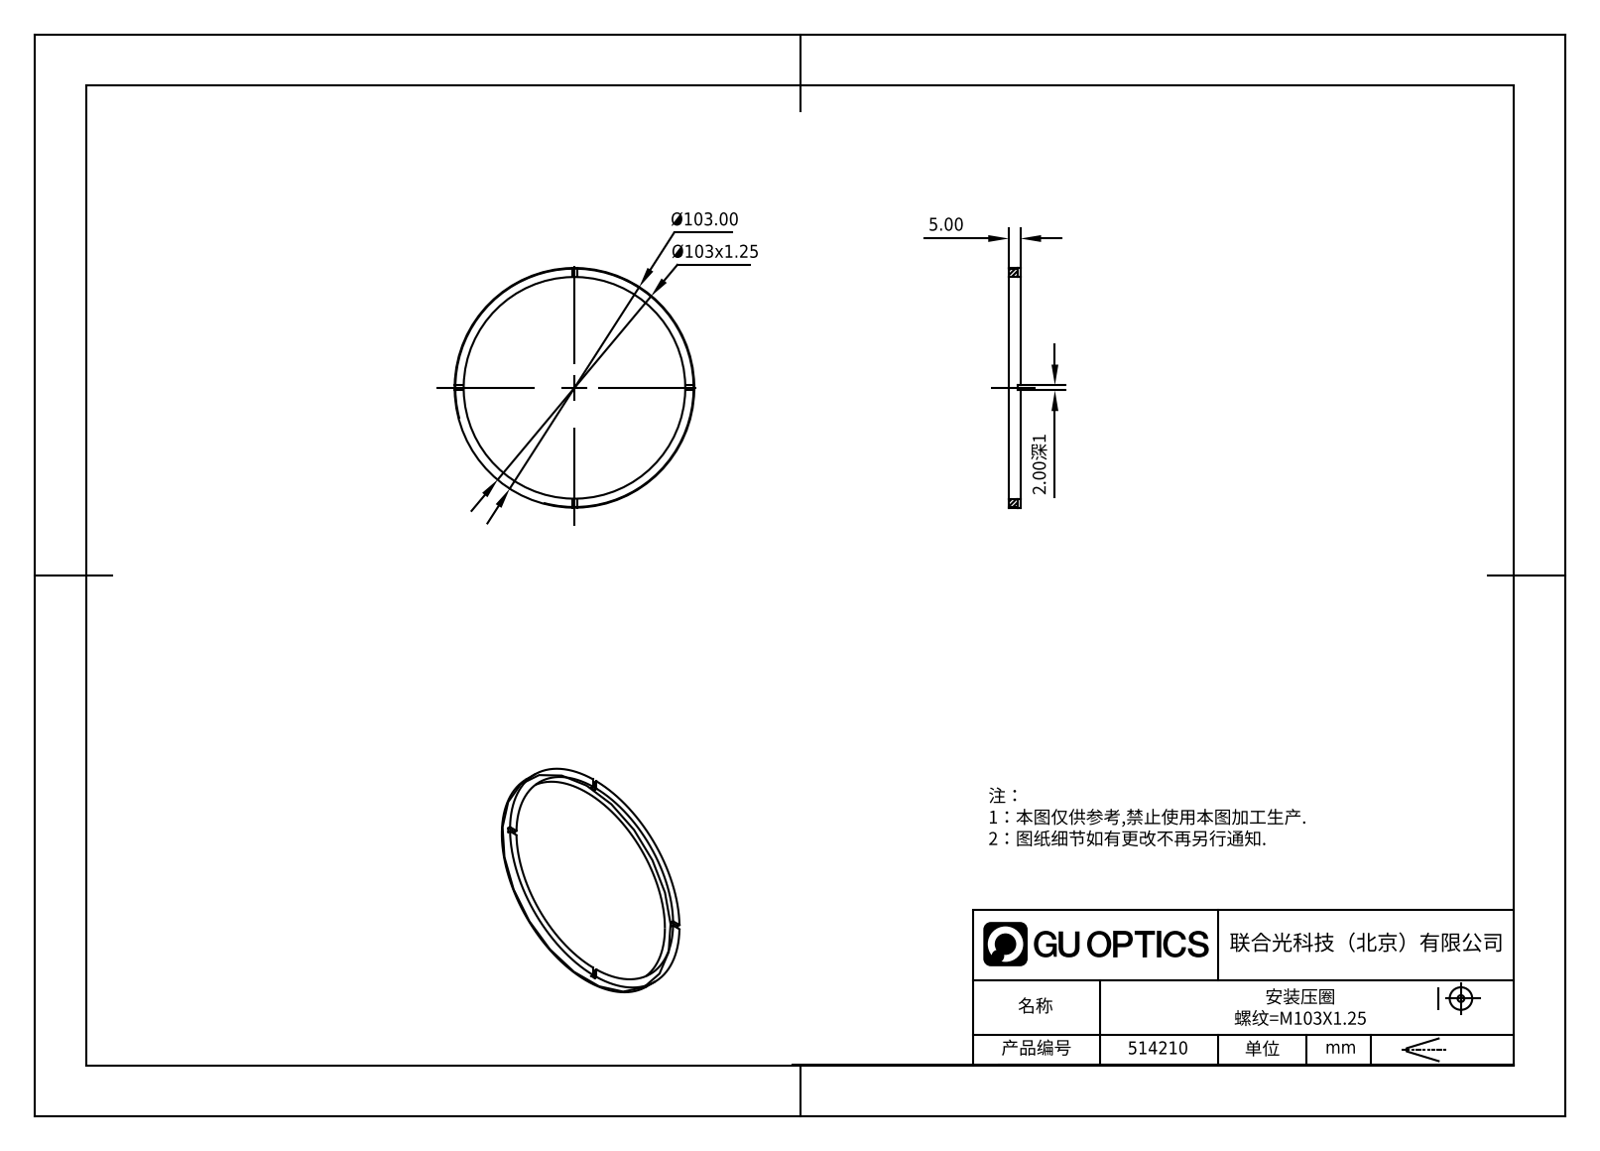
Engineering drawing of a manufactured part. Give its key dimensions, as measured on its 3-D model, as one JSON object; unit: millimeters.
{"part_name": "514210", "step_written_by": "SolidWorks 2020 (CONFIG_CONTROL_DESIGN)", "units": "millimeters", "bodies": {"solids": 1, "faces": 21, "planar": 17, "cylindrical": 4, "other": 0}, "overall_size": [103, 103, 5], "volume_mm3": 6188, "surface_area_mm2": 5614, "round_holes": [[95, 1]], "round_bosses_or_shafts": [[103, 1]], "face_to_face_distances": [5, 4, 1, 2]}
